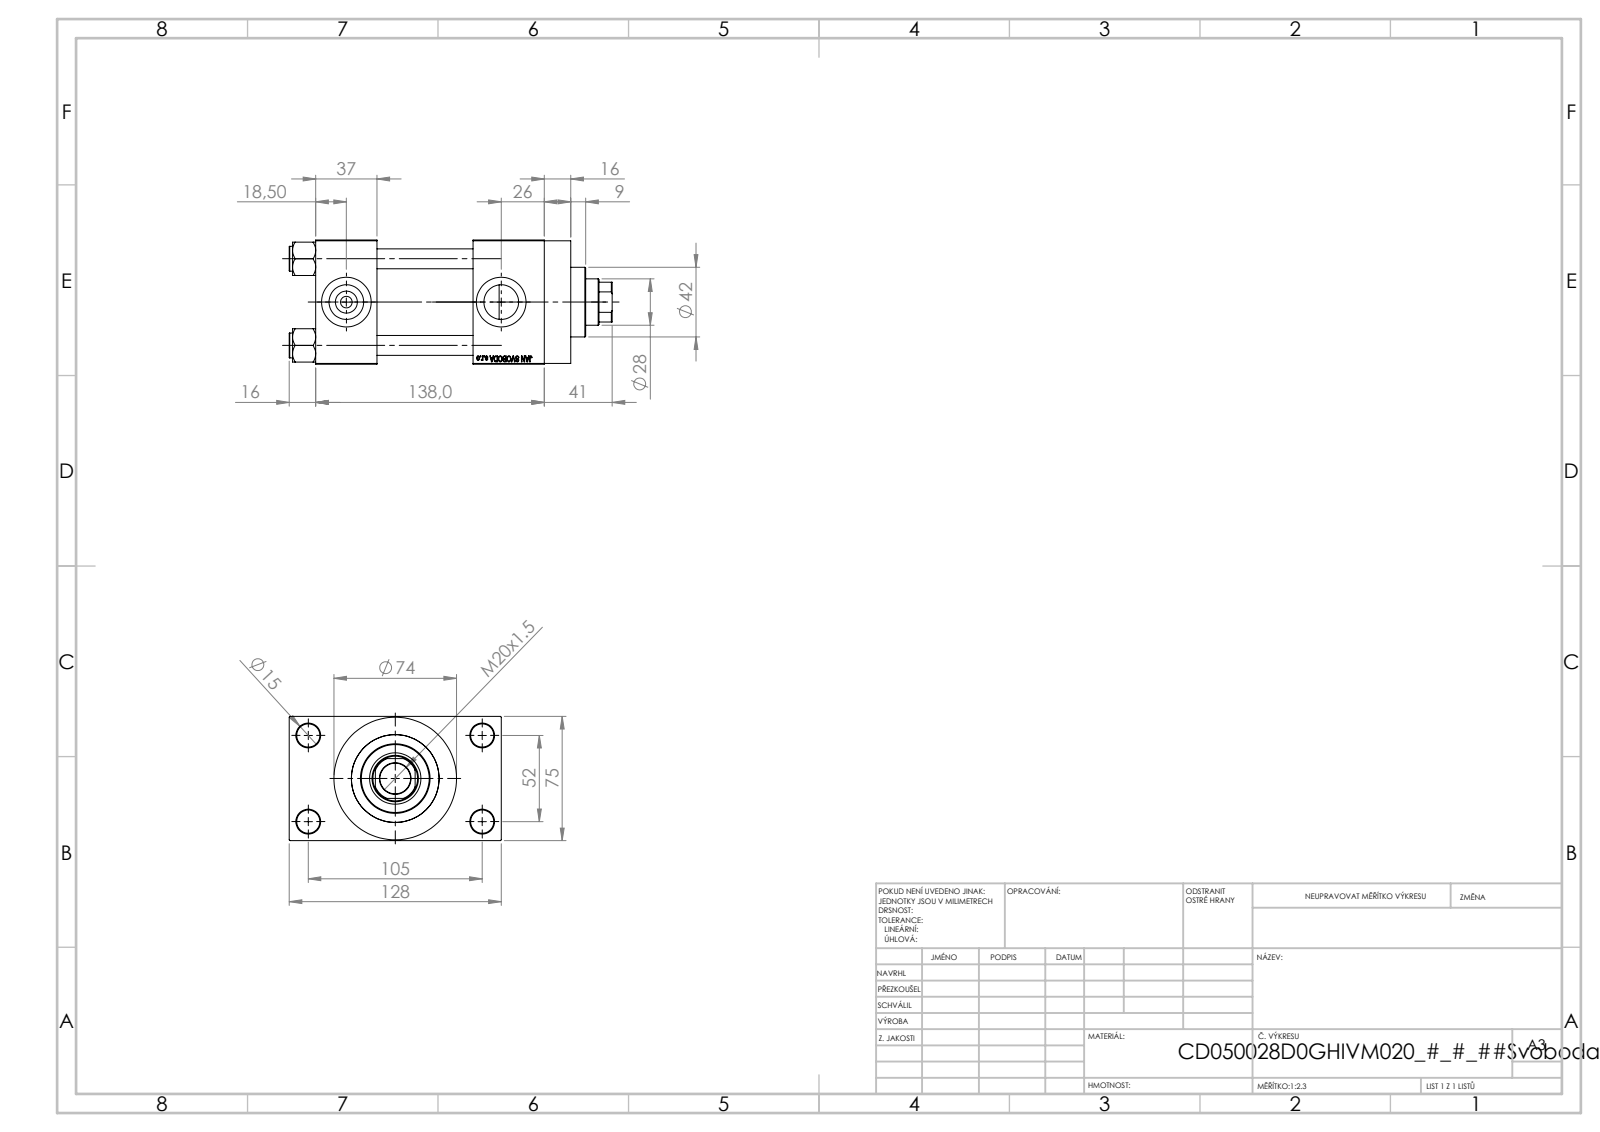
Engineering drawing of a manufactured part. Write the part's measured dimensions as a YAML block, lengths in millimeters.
part_name: "V215CD_VCP_D; V215CD_D_Body; V215CD_D_TYCINKA; V215CD_VC_A (+1 more)"
step_written_by: "SolidWorks 2019 (CONFIG_CONTROL_DESIGN)"
units: millimeters
bodies: {solids: 11, faces: 1103, planar: 497, cylindrical: 88, other: 518}
overall_size: [195, 128, 75]
volume: 806210
surface_area: 170608
round_holes:
  - {diameter: 12, count: 4}
  - {diameter: 14, count: 4}
  - {diameter: 7, count: 2}
  - {diameter: 20.96, count: 2}
  - {diameter: 30, count: 2}
  - {diameter: 18.5, count: 1}
  - {diameter: 28, count: 1}
  - {diameter: 31, count: 1}
  - {diameter: 41, count: 1}
  - {diameter: 50, count: 1}
  - {diameter: 53, count: 1}
round_bosses_or_shafts:
  - {diameter: 15, count: 4}
  - {diameter: 74, count: 1}
  - {diameter: 56, count: 1}
  - {diameter: 42, count: 1}
partial_cylinders:
  - {radius: 13.5, count: 1}
face_to_face_distances: [75, 58, 37, 95, 26.5, 138, 101, 43, 101.5, 16]
hole_center_spacings: [26.35, 36.98, 52.3, 58.43, 58.59, 78.65, 94.37, 52]
